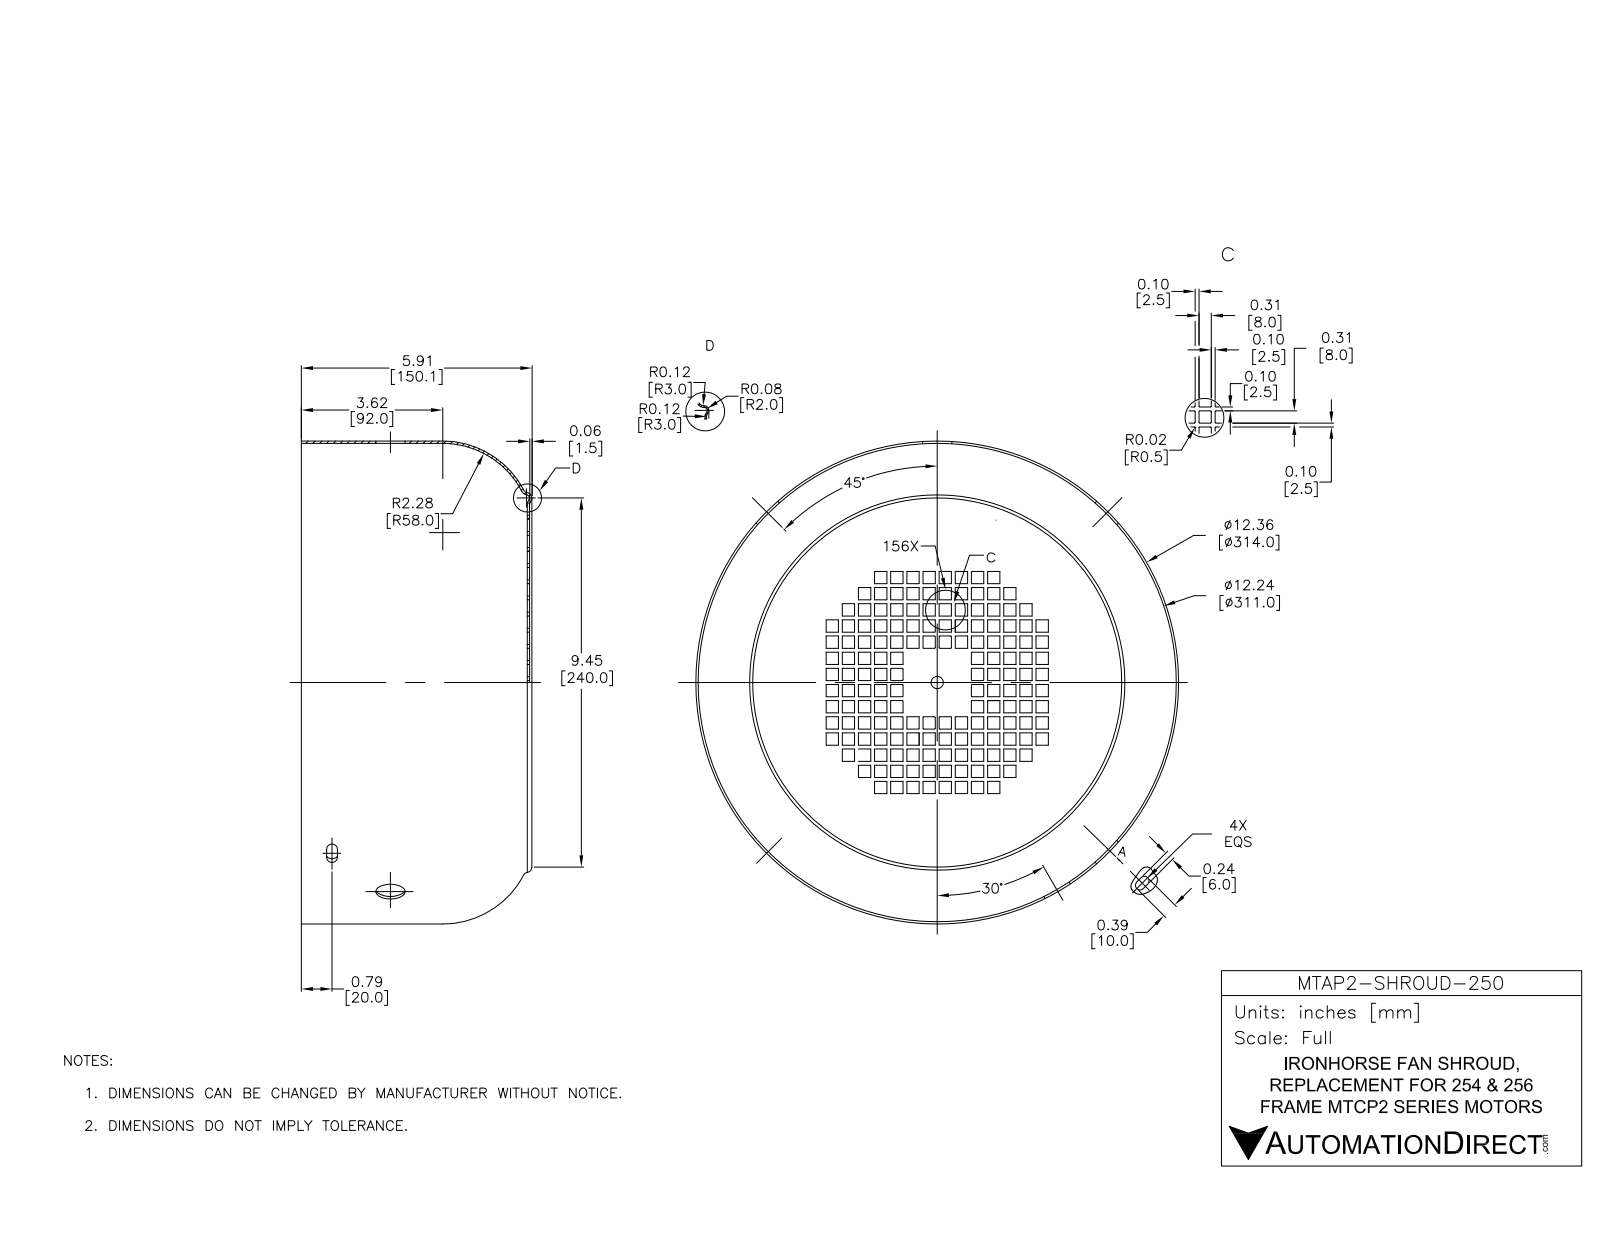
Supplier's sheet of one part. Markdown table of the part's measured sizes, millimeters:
| quantity | value |
| --- | --- |
| part name | MTAP2-SHROUD-250 |
| STEP written by | SolidWorks 2017 (AUTOMOTIVE_DESIGN) |
| units | millimeters |
| bodies | 1 solid, 829 faces (792 planar, 21 cylindrical, 16 other) |
| overall size | 314 × 314 × 150 |
| volume | 288 600 mm³ |
| surface area | 405 200 mm² |
| round holes (diameter × count) | 19 × 2, 8 × 1, 311 × 1 |
| round bosses / shafts (diameter × count) | 314 × 1 |
| partial cylindrical surfaces (radius × count) | 3.5 × 7 |
| main face-to-face distances | 1.5, 0.5, 1, 10, 20, 8, 147, 147.5, 148.5, 80 |
